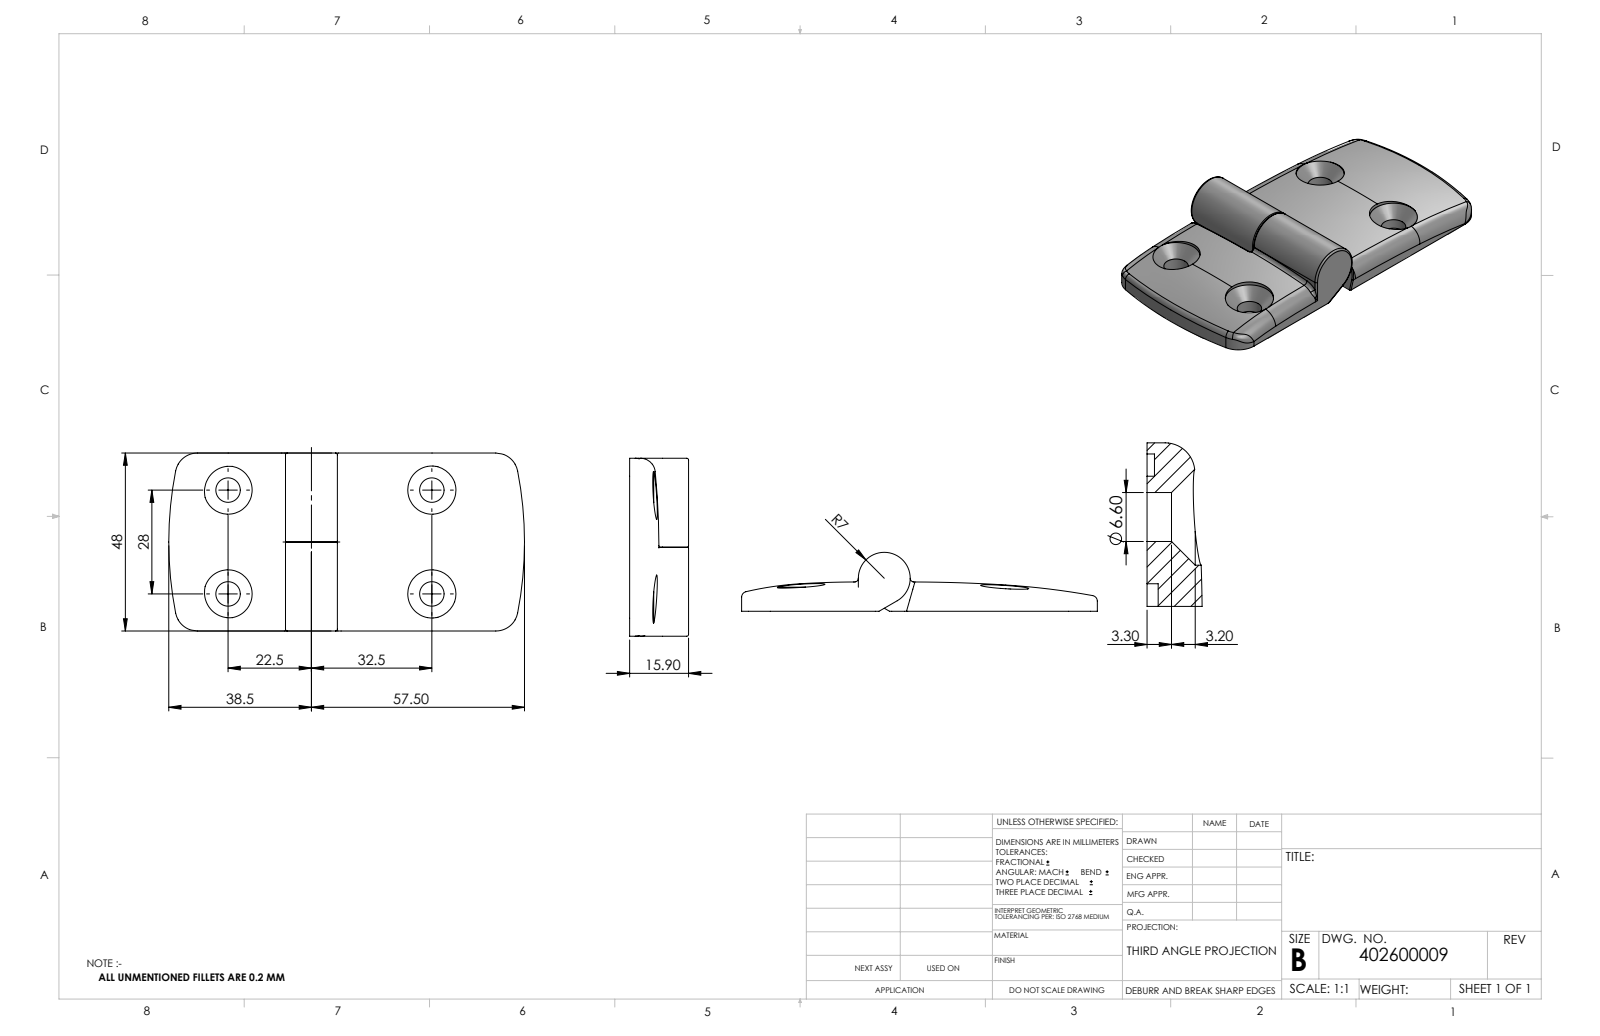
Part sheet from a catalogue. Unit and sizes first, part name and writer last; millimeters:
Units: millimetres
Overall size (bounding box): 96 × 48 × 16.2
Round holes (diameter × count): ⌀6.6 ×4, ⌀13 ×2, ⌀6 ×1
Round bosses / shafts (diameter × count): ⌀14 ×1
Partial cylindrical surfaces — rounded edges, fillets, slot ends (radius × count): R0.3 ×6, R0.5 ×6, R6 ×4, R4 ×2, R6.5 ×2, R100 ×2
Main face-to-face distances: 1, 24, 1.5, 2, 5, 3, 48, 17, 22, 0.5
Hole centre spacings: 28, 55, 61.72
Volume: 29 322 mm³ · Surface area: 14 475 mm²
Bodies: 3 solids, 195 faces (82 planar, 49 cylindrical, 64 other)
Part name (STEP PRODUCT): 402600009_c_1
STEP written by: SolidWorks 2014 (CONFIG_CONTROL_DESIGN)
